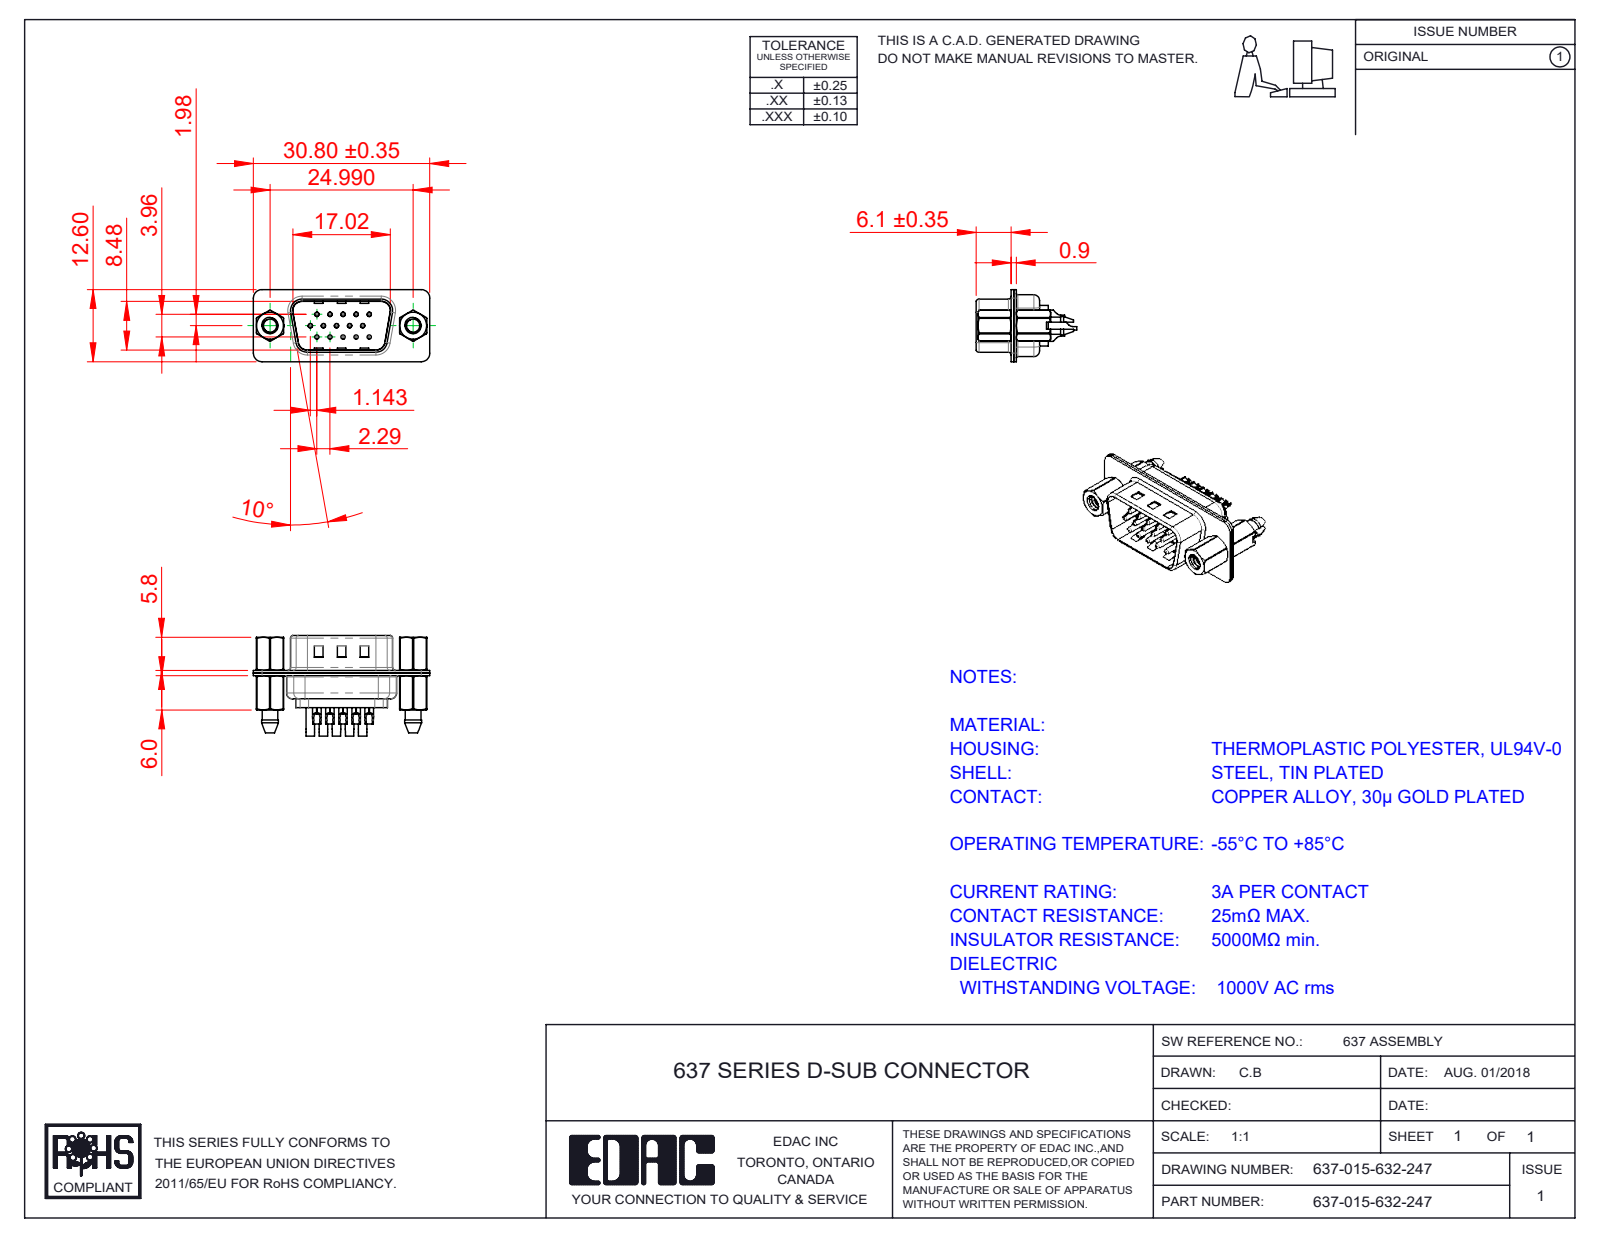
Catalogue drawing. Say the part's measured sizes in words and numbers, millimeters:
The part is named "637 Shell Front_15 Contacts; 637 Contact Row 2_32; 637 Contact Row 1_32; 637 Housing_15 Contacts (+5 more)". Its 3-D file was written by "SolidWorks 2020 (CONFIG_CONTROL_DESIGN)". It is 22 solids with 1464 faces: 371 planar, 668 cylindrical and 425 other. Overall it measures 30.8 by 17.55 by 12.6 millimeters. Its volume is 1 656 cubic millimeters and its surface area 5 547 square millimeters. Round holes: 15 of diameter 0.35, 15 of diameter 1.1, 15 of diameter 1.6, 2 of diameter 2.26, 2 of diameter 2.29, 2 of diameter 4, 2 of diameter 4.8. Round bosses or shafts: 15 of diameter 2, 15 of diameter 1.5, 15 of diameter 0.75, 2 of diameter 4.9, 2 of diameter 2.79. Partial cylindrical surfaces (rounded edges, fillets, slot ends): 18 of radius 1.5, 12 of radius 2, 8 of radius 0.5, 7 of radius 1, 6 of radius 1.6, 4 of radius 0.25, 4 of radius 0.55, 4 of radius 0.7. The main face-to-face distances are 0.45, 0.4, 0.9, 0.7, 4.76, 8.88, 8.48, 6.5, 1.05, 4.55. The hole center spacings are 3.96, 2.28, 4.57, 2.29, 6.05, 6.86, 7.92, 6.04.
